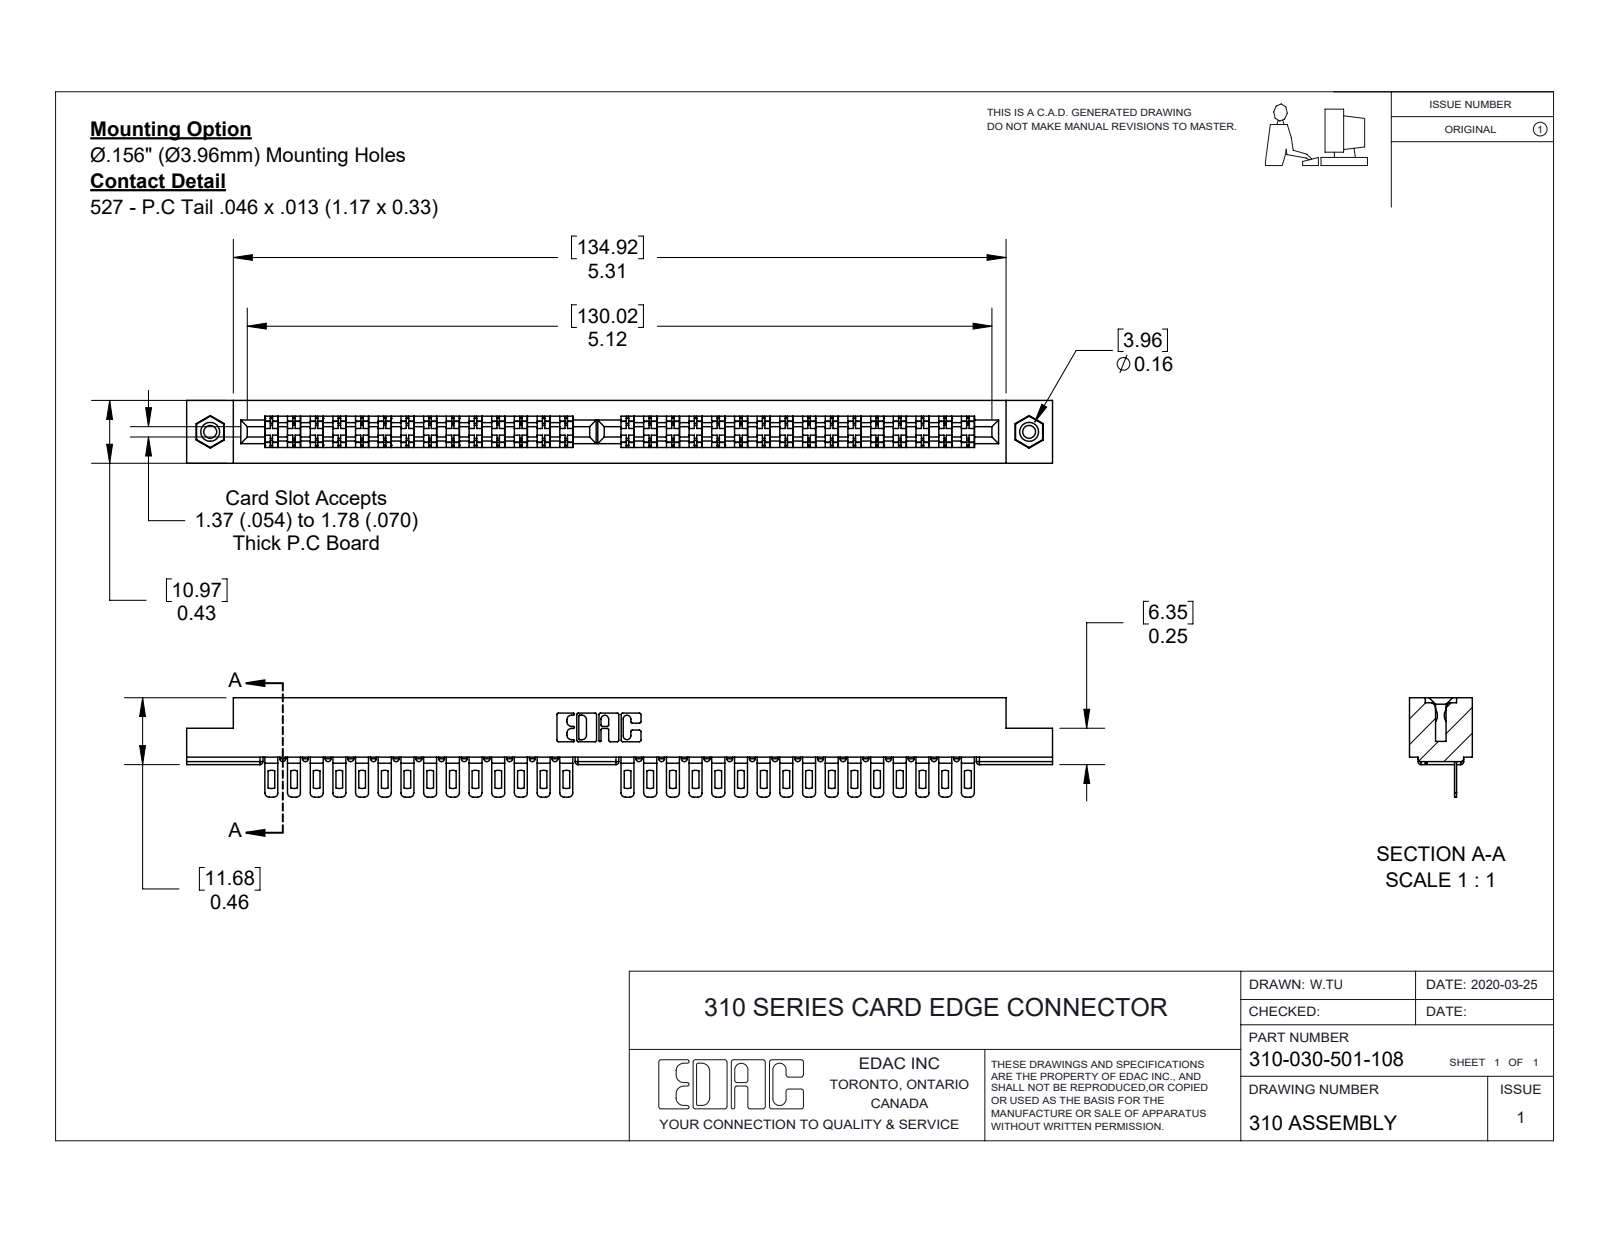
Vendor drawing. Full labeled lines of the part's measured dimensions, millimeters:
Part name (STEP PRODUCT): 307-290-002_501; 310 Part_.116 Hex; 310-030-501-108; 345-250-001_345-250-003-102
STEP written by: SolidWorks 2016 (CONFIG_CONTROL_DESIGN)
Units: millimetres
Bodies: 33 solids, 2506 faces (1436 planar, 990 cylindrical, 80 other)
Overall size (bounding box): 151.21 × 17.37 × 10.97
Volume: 13 121 mm³ · Surface area: 18 627 mm²
Round holes (diameter × count): ⌀2.26 ×2, ⌀3.17 ×2, ⌀3.96 ×2
Round bosses / shafts (diameter × count): ⌀3.94 ×2
Partial cylindrical surfaces — rounded edges, fillets, slot ends (radius × count): R0.51 ×98, R0.76 ×60, R1.57 ×60, R0.25 ×22, R0.17 ×6, R0.8 ×6, R0.67 ×3, R0.31 ×2
Main face-to-face distances: 2.76, 8.22, 0.33, 5.13, 3.09, 7.89, 10.98, 5.46, 1.24, 3.89
Hole centre spacings: 143
